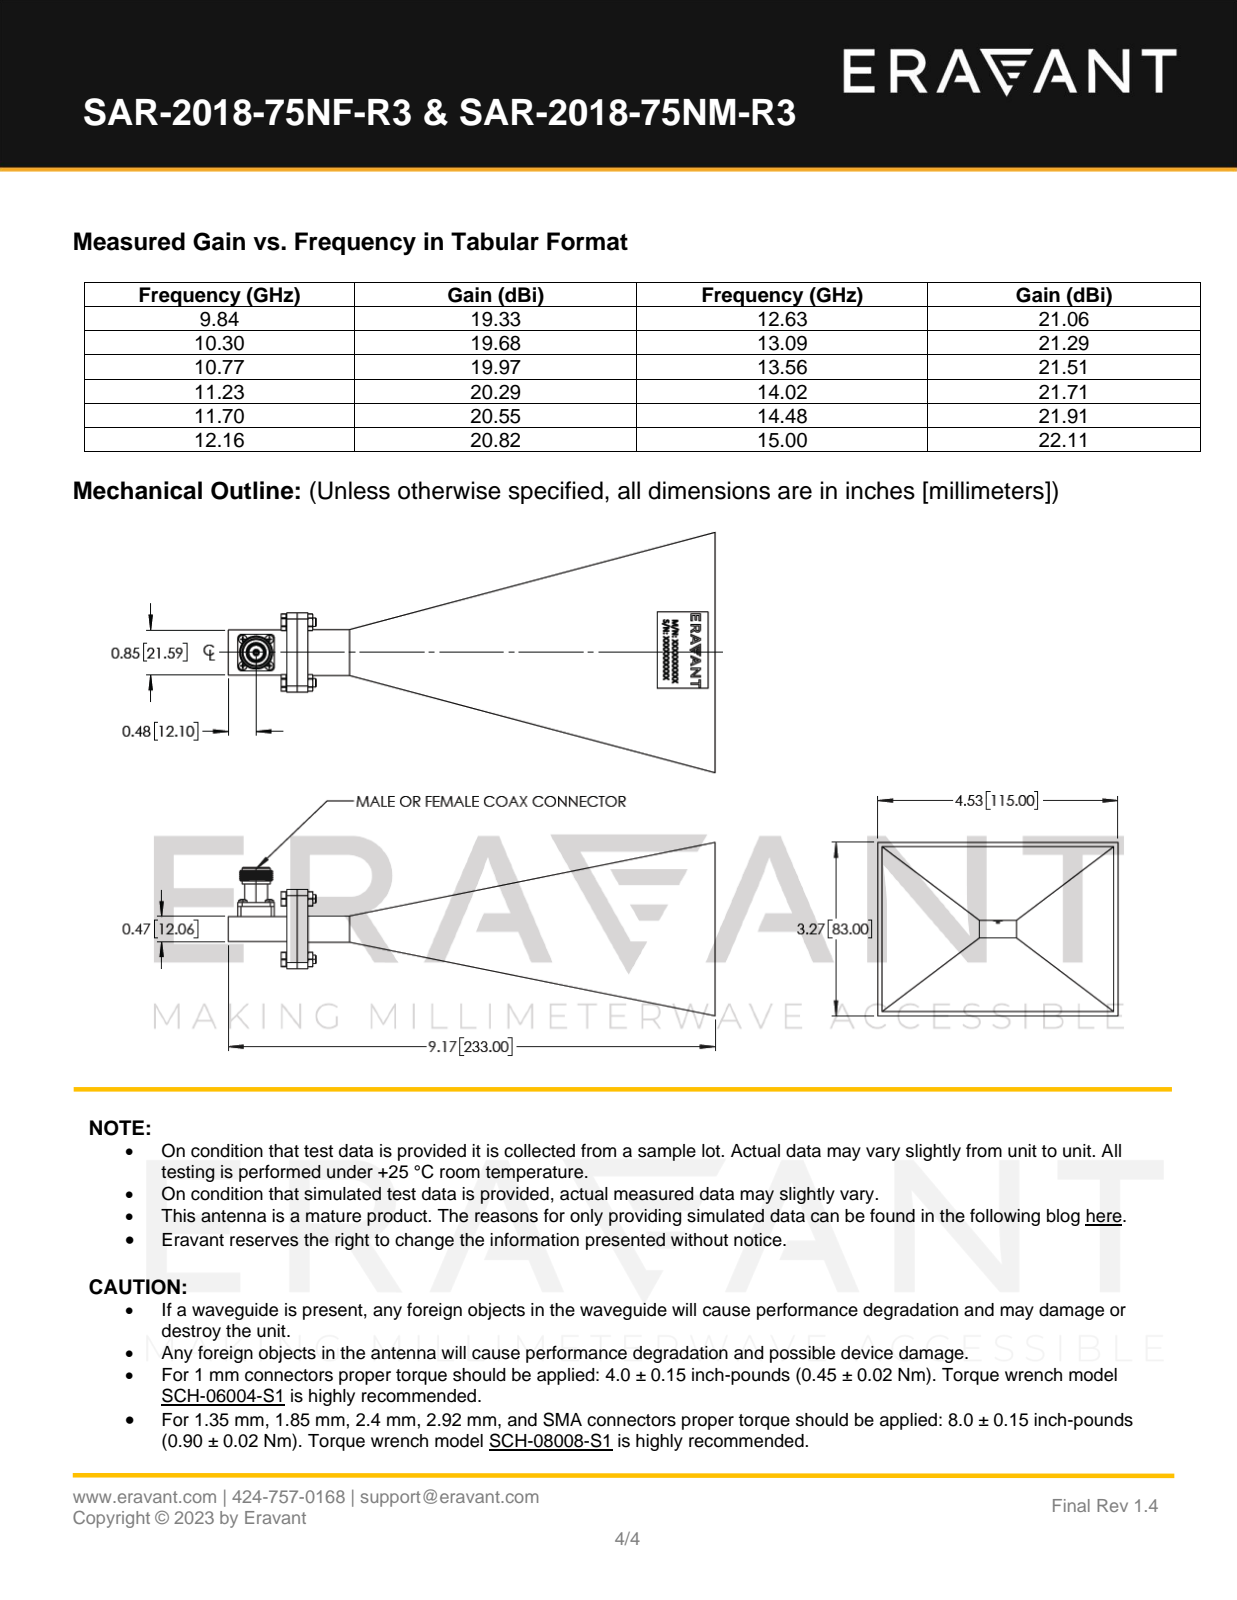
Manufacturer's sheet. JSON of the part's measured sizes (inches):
{"part_name": "AR-7C1-R-H1, Female", "step_written_by": "SolidWorks 2021 (AUTOMOTIVE_DESIGN)", "units": "inches", "bodies": {"solids": 11, "faces": 492, "planar": 230, "cylindrical": 186, "other": 76}, "overall_size": [9.173, 4.528, 3.268], "volume_in3": 42.78, "surface_area_in2": 102.3, "round_holes": [[0.093, 4], [0.102, 4], [0.169, 4], [0.173, 4], [0.018, 1], [0.12, 1], [0.276, 1], [0.31, 1]], "round_bosses_or_shafts": [[0.157, 8], [0.354, 4], [0.26, 4], [0.132, 4], [0.079, 4], [0.625, 1], [0.546, 1], [0.531, 1]], "partial_cylinders_radius": [[0.012, 16], [0.118, 4], [0.433, 1], [0.453, 1]], "face_to_face_distances": [7.874, 0.197, 7.677, 0.394, 8.071, 1.496, 0.475, 0.511, 0.985, 0.85], "hole_center_spacings": [0.354, 0.5, 0.707, 1.04, 1.122, 1.53]}
